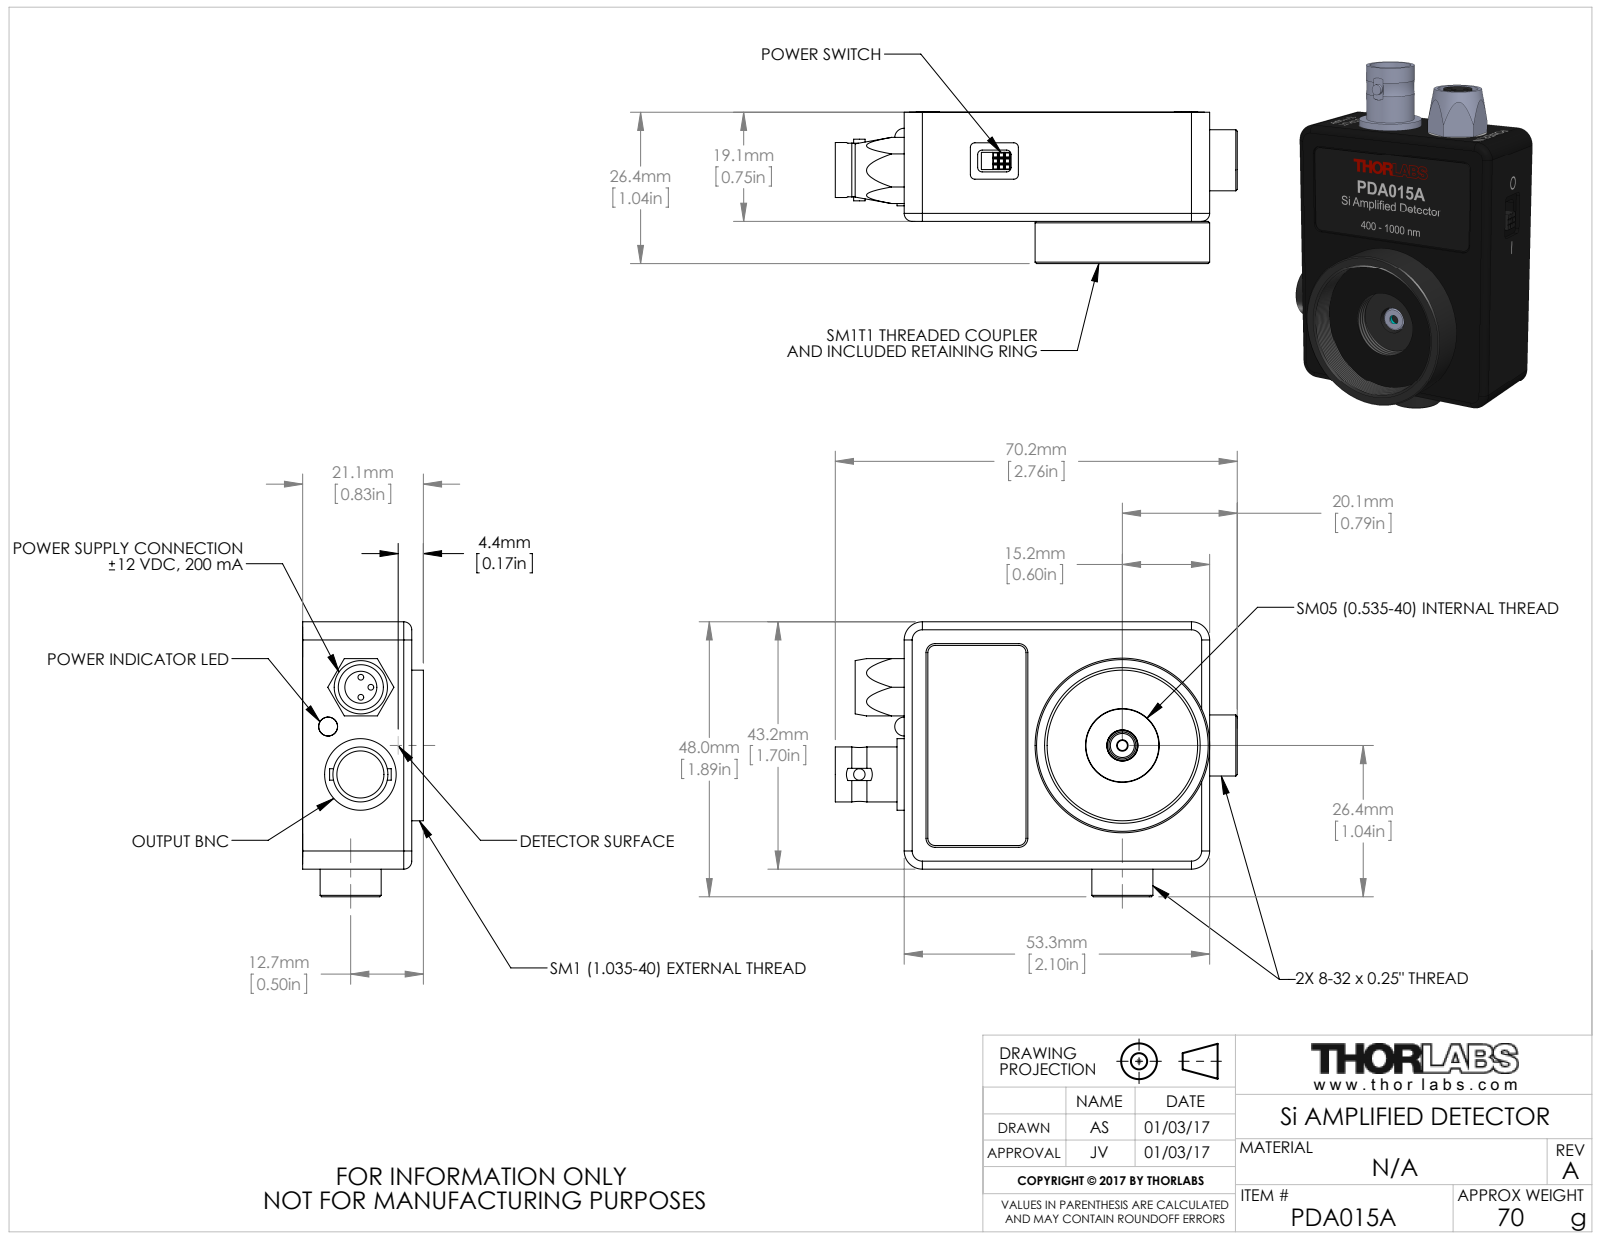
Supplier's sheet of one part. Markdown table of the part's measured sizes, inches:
| quantity | value |
| --- | --- |
| part name | PDA015A |
| STEP written by | SolidWorks 2014 (AUTOMOTIVE_DESIGN) |
| units | inches |
| bodies | 0 solids, 319 faces (186 planar, 80 cylindrical, 53 other) |
| overall size | 2.763 × 1.89 × 1.041 |
| round holes (diameter × count) | 0.039 × 3, 0.136 × 2, 0.069 × 1, 0.079 × 1, 0.214 × 1, 0.31 × 1, 0.324 × 1, 0.507 × 1, 1.035 × 1 |
| round bosses / shafts (diameter × count) | 0.42 × 2, 1.2 × 1, 0.492 × 1, 0.378 × 1, 0.22 × 1, 0.185 × 1, 0.079 × 1 |
| partial cylindrical surfaces (radius × count) | 0.031 × 8, 0.05 × 4, 0.055 × 4, 0.095 × 4, 0.1 × 4, 0.125 × 4, 0.063 × 2, 0.063 × 2 |
| main face-to-face distances | 0.751, 1.7, 0.731, 0.02, 0.743, 2.1, 0.831, 0.1, 0.088, 0.08 |
| hole center spacings | 0.069, 0.097, 0.138, 0.21, 0.339, 0.406, 0.424, 0.474 |
